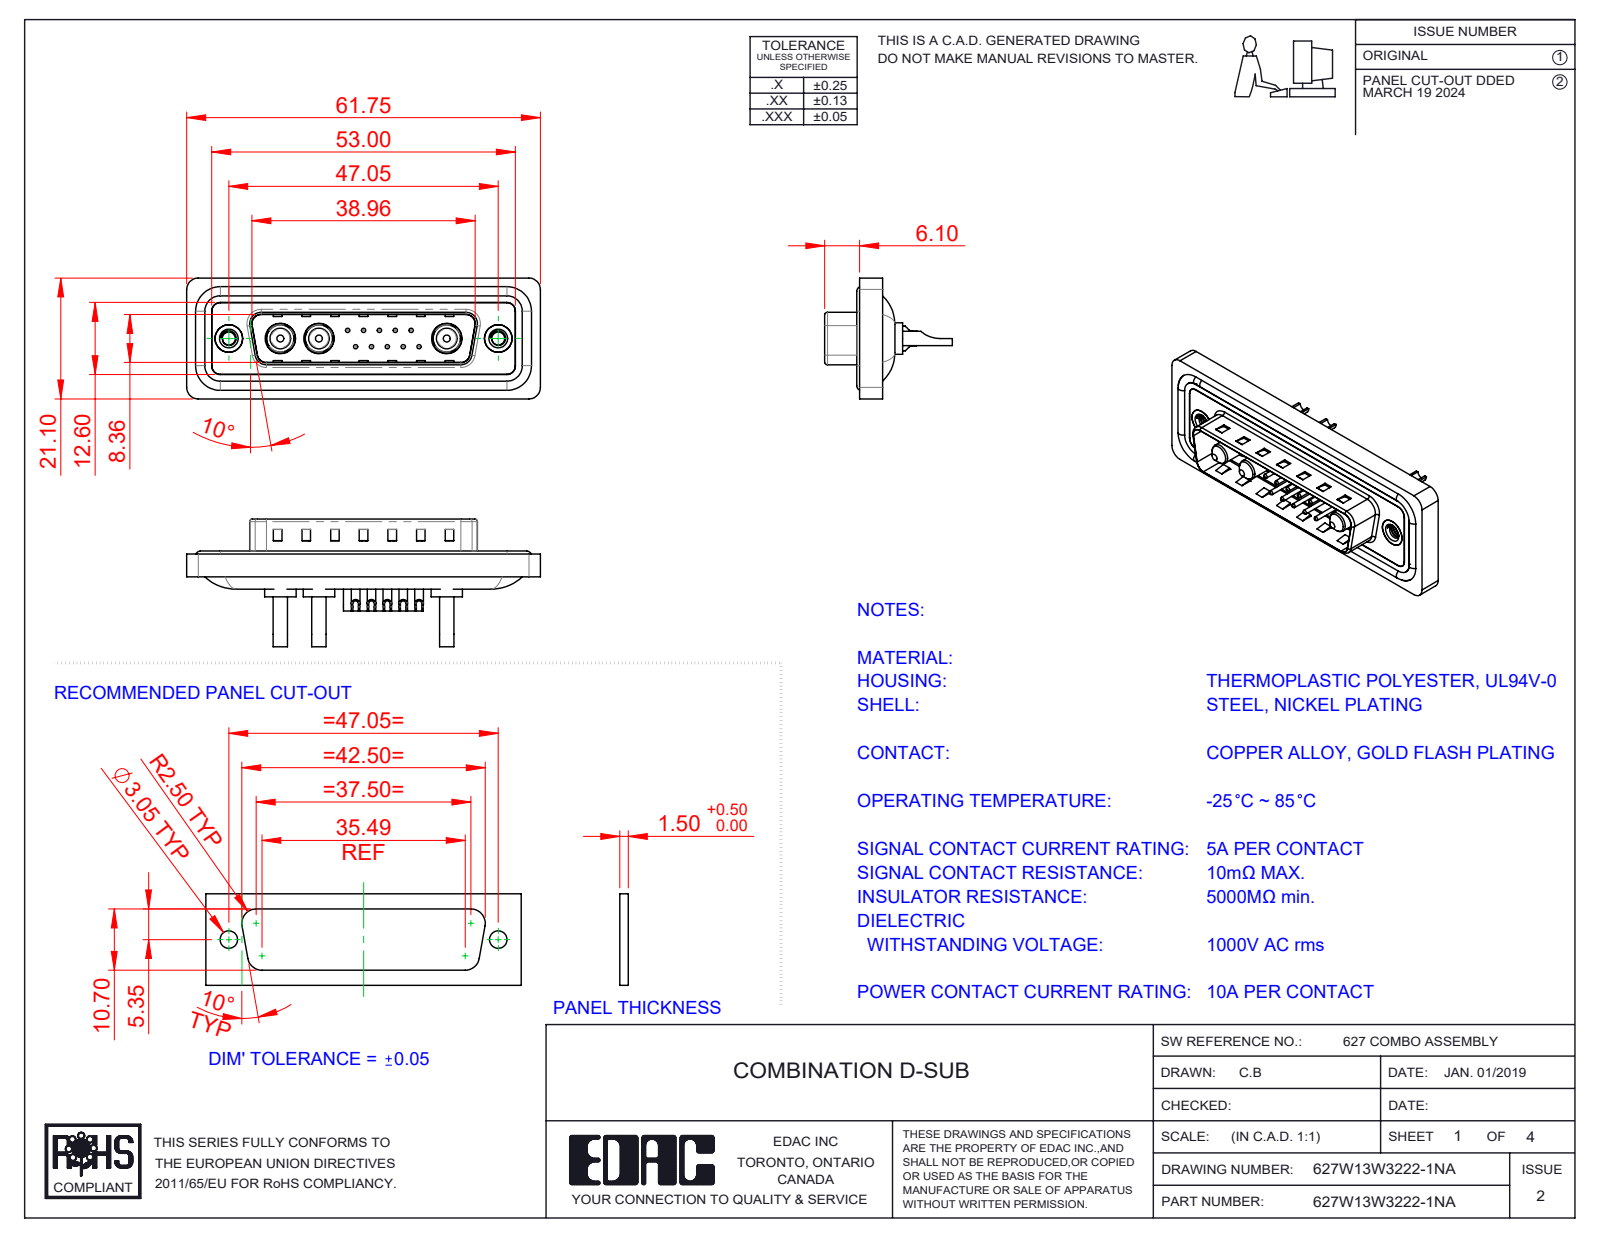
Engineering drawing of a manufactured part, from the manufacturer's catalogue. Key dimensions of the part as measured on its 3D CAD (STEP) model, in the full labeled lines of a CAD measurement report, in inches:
Part name (STEP PRODUCT): 627Combo Shell Rear_25 Contacts; 627W13W3222-1NA; 627Combo Contact Row 1_22; 627Combo Threaded Rivet_A (+5 more)
STEP written by: SolidWorks 2023 (CONFIG_CONTROL_DESIGN)
Units: inches
Bodies: 23 solids, 986 faces (335 planar, 416 cylindrical, 235 other)
Overall size (bounding box): 2.431 × 0.878 × 0.831
Volume: 0.448 in³ · Surface area: 18.75 in²
Round holes (diameter × count): ⌀0.03 ×10, ⌀0.039 ×10, ⌀0.063 ×10, ⌀0.079 ×10, ⌀0.067 ×3, ⌀0.191 ×3, ⌀0.209 ×3, ⌀0.089 ×2, ⌀0.157 ×2, ⌀0.189 ×2, ⌀0.197 ×2
Round bosses / shafts (diameter × count): ⌀0.059 ×10, ⌀0.063 ×4, ⌀0.217 ×3, ⌀0.205 ×3, ⌀0.187 ×3, ⌀0.148 ×3, ⌀0.142 ×3, ⌀0.098 ×3
Partial cylindrical surfaces — rounded edges, fillets, slot ends (radius × count): R0.059 ×22, R0.079 ×18, R0.02 ×8, R0.063 ×8, R0.039 ×6, R0.01 ×4, R0.024 ×4, R0.026 ×4
Main face-to-face distances: 0.016, 0.059, 0.043, 0.063, 0.02, 0.122, 0.114, 0.032, 0.377, 0.161
Hole centre spacings: 0.124, 0.109, 0.198, 0.218, 0.295, 0.198, 0.327, 0.398
